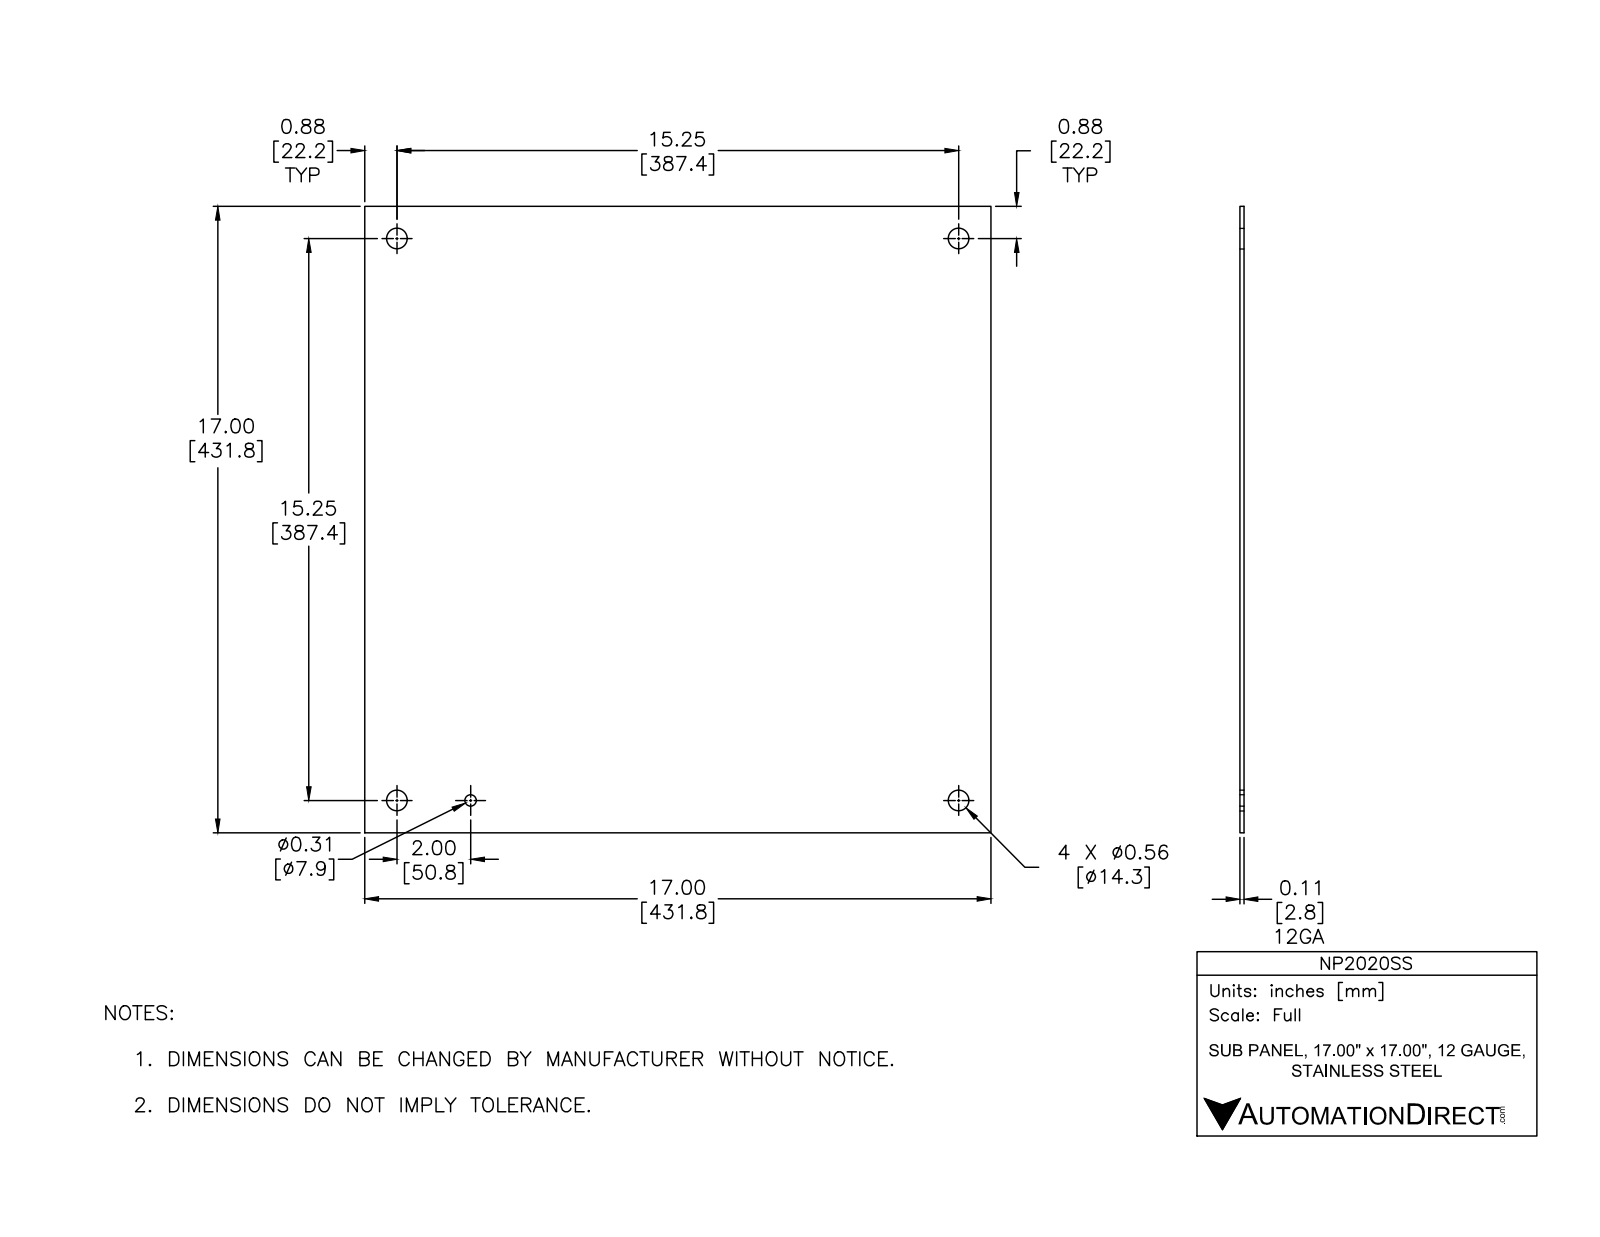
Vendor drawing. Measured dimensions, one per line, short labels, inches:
name: NP2020SS
written by: Autodesk Inventor 2012 (AUTOMOTIVE_DESIGN)
unit: in
bodies: 1 solid, 11 faces (6 planar, 5 cylindrical, 0 other)
size: 17 × 17 × 0.094
volume: 26.98 in³; area: 583 in²
holes: 4× ⌀0.563, 1× ⌀0.31
face distances: 0.094, 17
hole spacings: 15.25, 2, 13.25, 15.25, 15.381, 20.202, 21.567, 21.567
